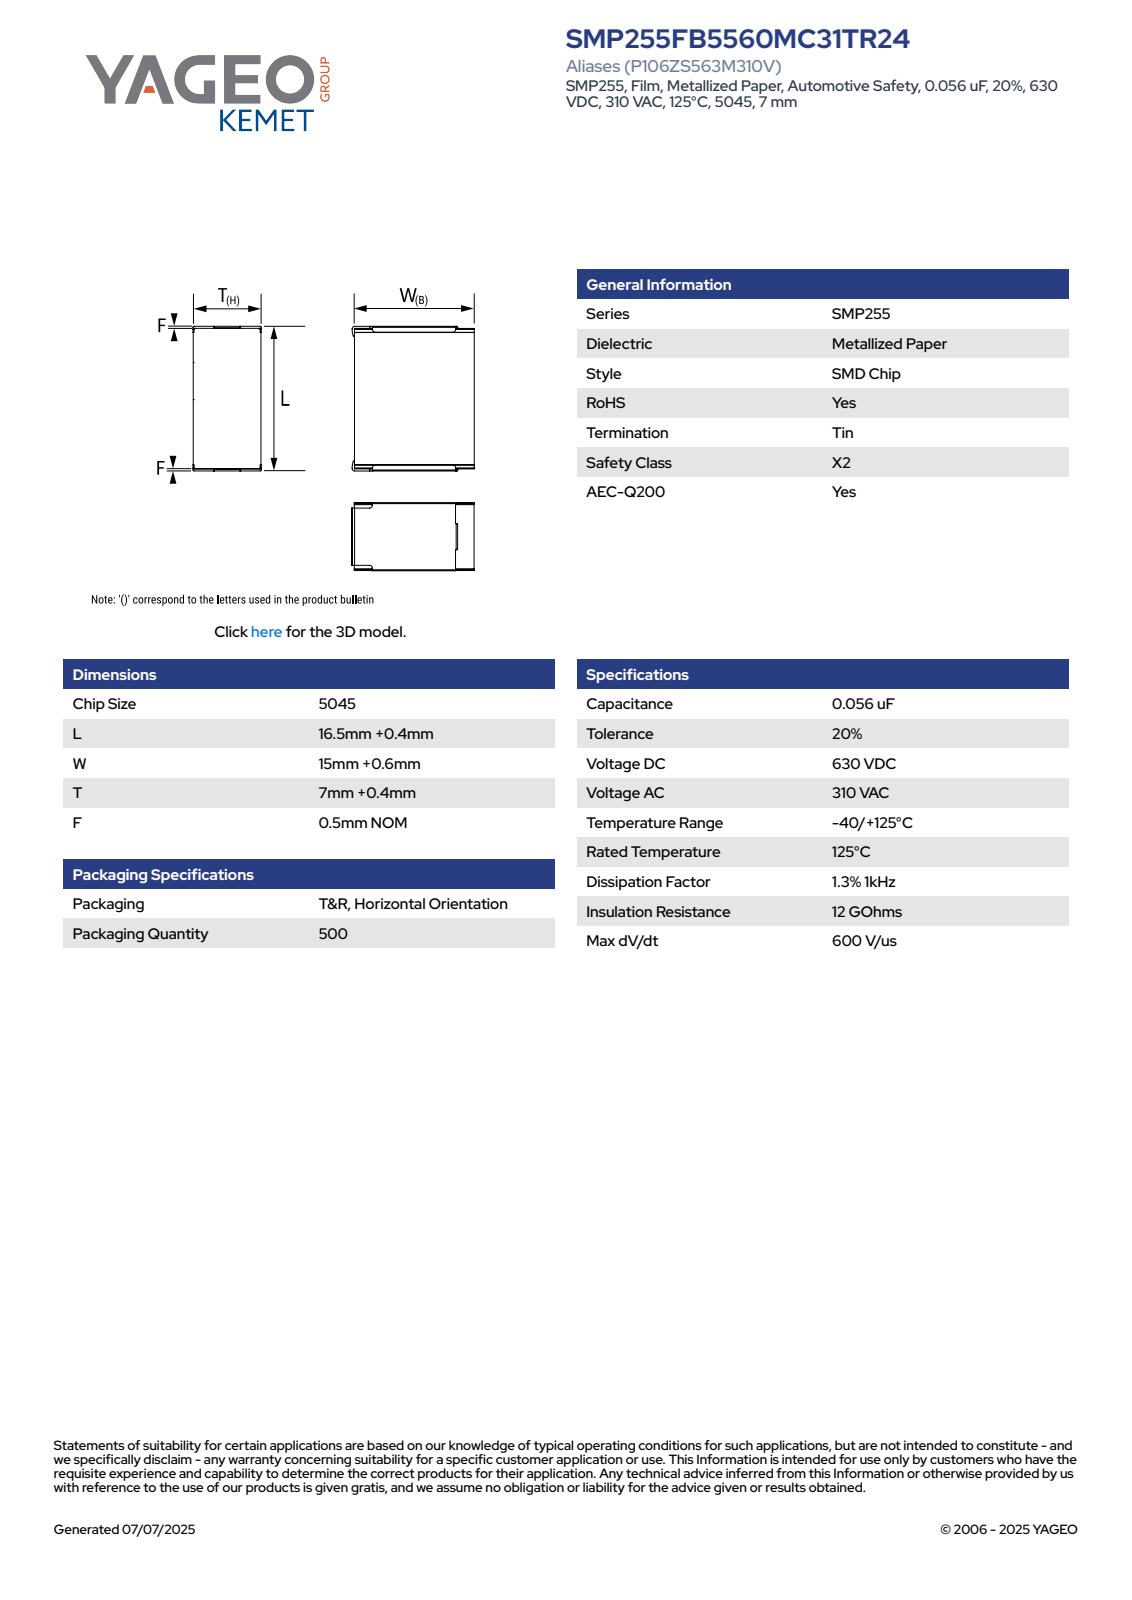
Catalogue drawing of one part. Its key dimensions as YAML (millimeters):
part_name: "CFS_KSTD_5045_L16.9W15.6T7.4F0.5"
step_written_by: "SolidWorks 2021 (AUTOMOTIVE_DESIGN)"
units: millimeters
bodies: {solids: 4, faces: 117, planar: 103, cylindrical: 14, other: 0}
overall_size: [16.9, 16.12, 7.78]
volume: 1900
surface_area: 1071
partial_cylinders:
  - {radius: 0.44, count: 10}
  - {radius: 0.59, count: 4}
face_to_face_distances: [7.4, 16.9, 14.98, 0.5, 16.4, 7.59, 0.62, 15.9, 7.78, 15.6]
